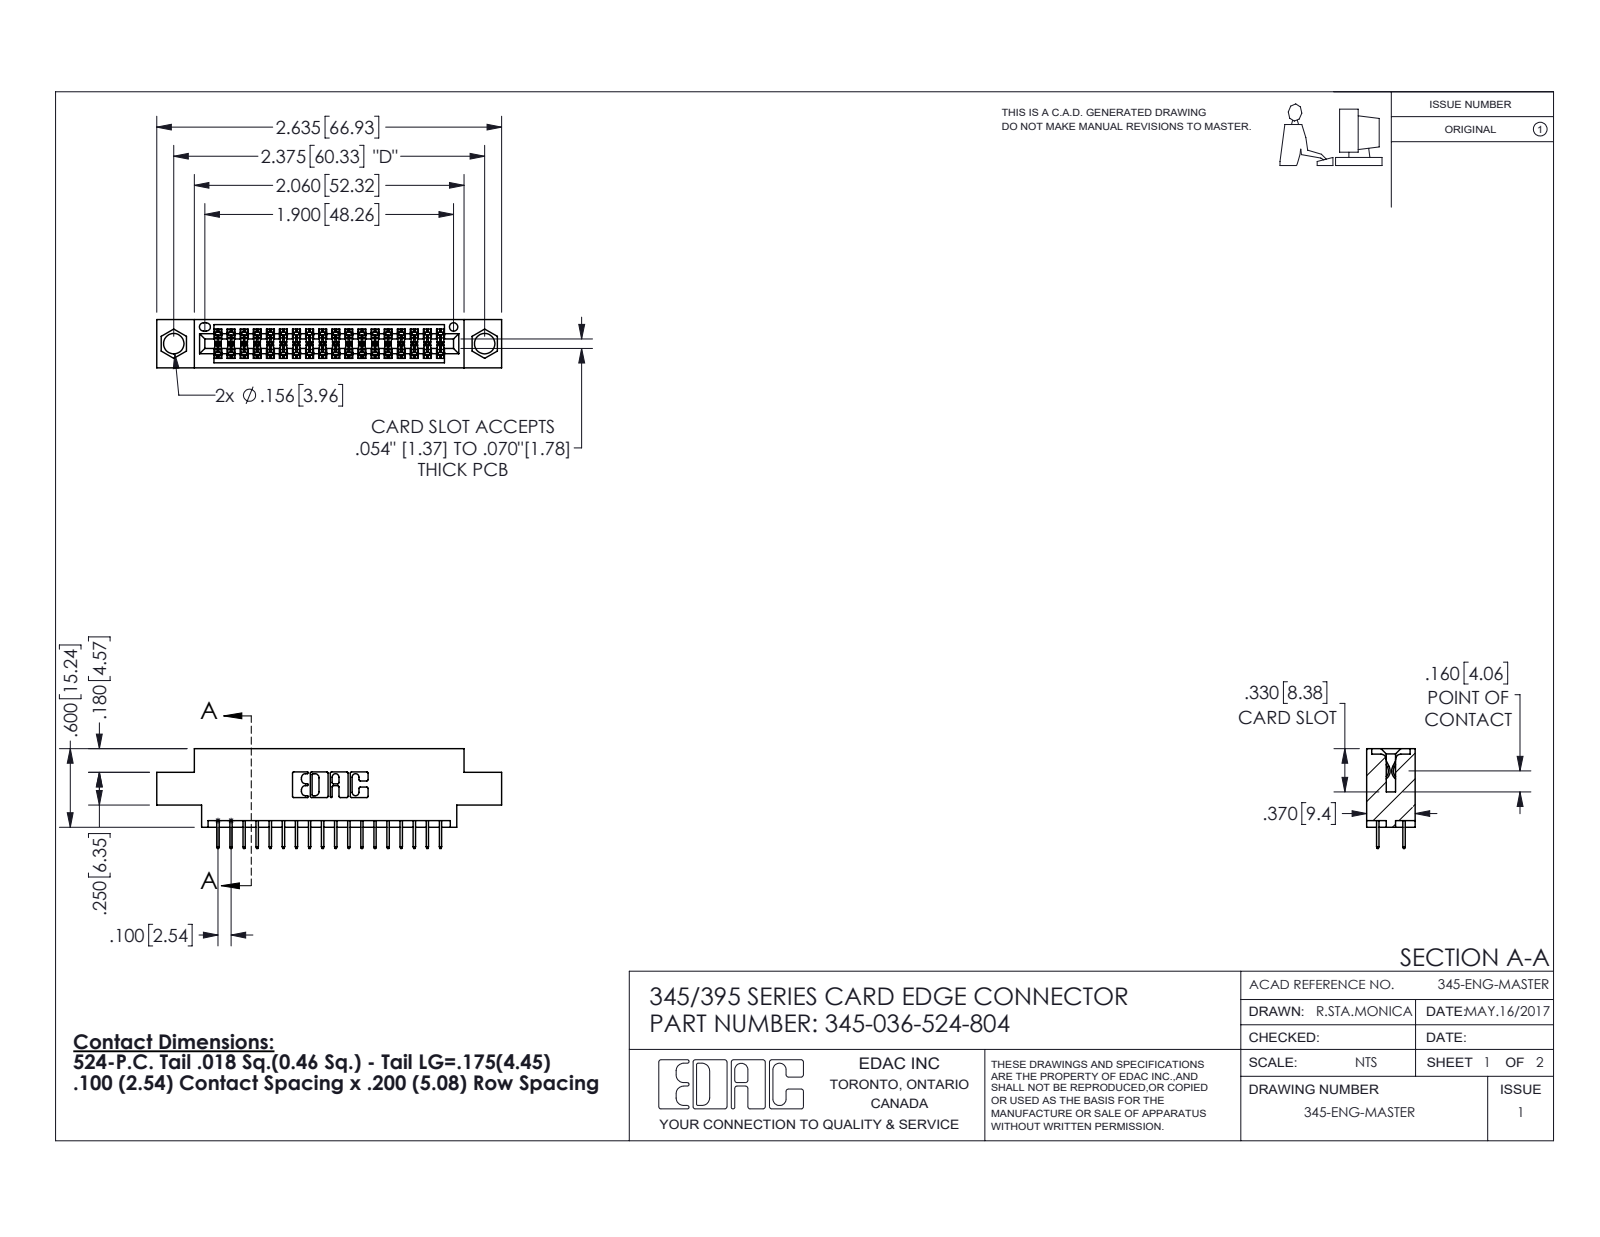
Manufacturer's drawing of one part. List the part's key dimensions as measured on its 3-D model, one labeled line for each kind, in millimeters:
Part name (STEP PRODUCT): 345 Part_0.170 Offset - 0.156 Dia-TI; 345-292-001_345-293-124; 345-036-524-804
STEP written by: SolidWorks 2020 (CONFIG_CONTROL_DESIGN)
Units: millimetres
Bodies: 37 solids, 2088 faces (1502 planar, 586 cylindrical, 0 other)
Overall size (bounding box): 66.9 × 19.4 × 9.4
Volume: 6 000 mm³ · Surface area: 8 264 mm²
Round holes (diameter × count): ⌀4 ×2, ⌀1.6 ×1
Partial cylindrical surfaces — rounded edges, fillets, slot ends (radius × count): R0.2 ×54, R0.3 ×22, R0.2 ×6, R0.8 ×6, R0.7 ×3, R0.4 ×2, R0.5 ×2, R0.6 ×2
Main face-to-face distances: 1.8, 7.6, 9.4, 5.1, 2.5, 6.9, 0.6, 5.7, 4.4, 1.8
Hole centre spacings: 6.9, 54.4, 60.3
